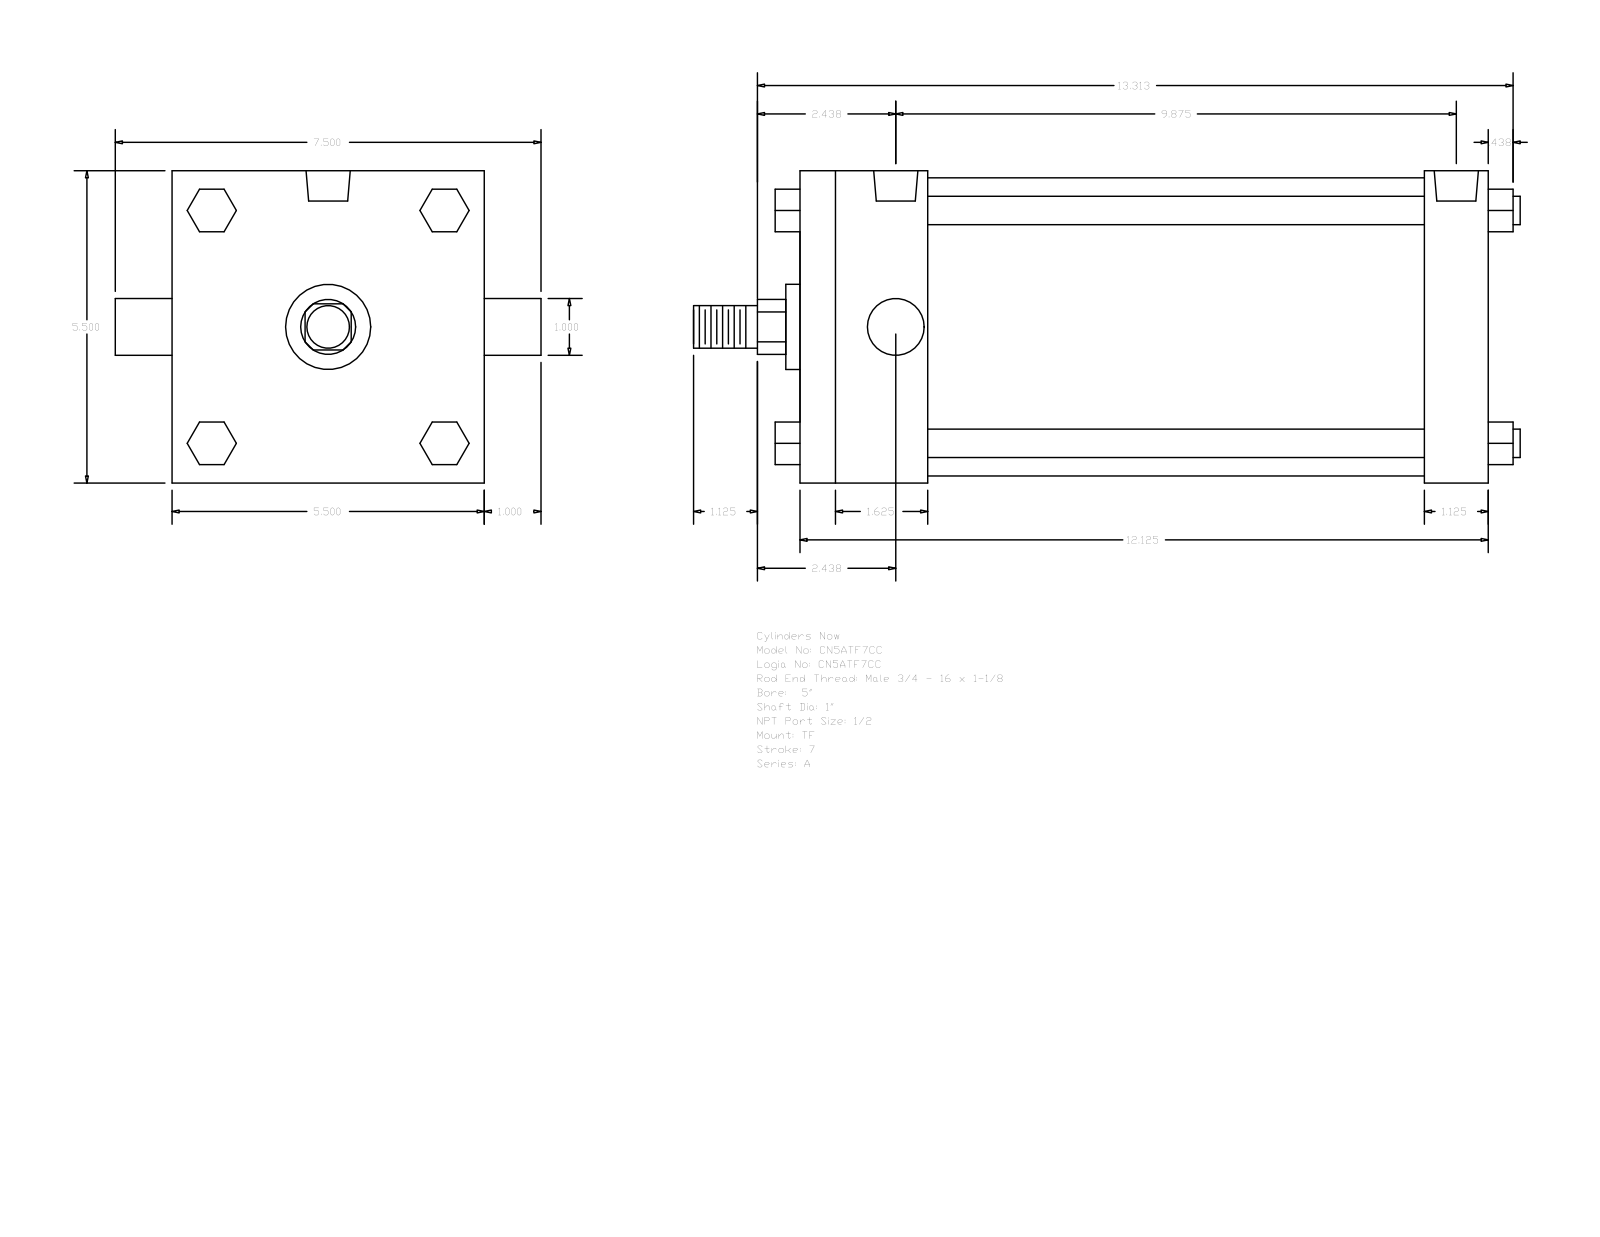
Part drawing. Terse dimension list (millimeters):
name: A_TF__0500_1
written by: GSSL Pune (CONFIG_CONTROL_DESIGN)
unit: mm
bodies: 0 solids, 120 faces (92 planar, 28 cylindrical, 0 other)
size: 369.89 × 190.5 × 139.7
holes: 3× ⌀8.73, 2× ⌀19.77
bosses: 4× ⌀12.7, 2× ⌀25.4, 1× ⌀133.35, 1× ⌀38.1, 1× ⌀19.05
rounds: 1× R12.29
face distances: 139.7, 307.97, 28.57, 279.4, 57.15, 222.25, 250.82, 19.05, 52.07, 90.18
hole spacings: 2.39, 248.44, 246.05, 250.83
